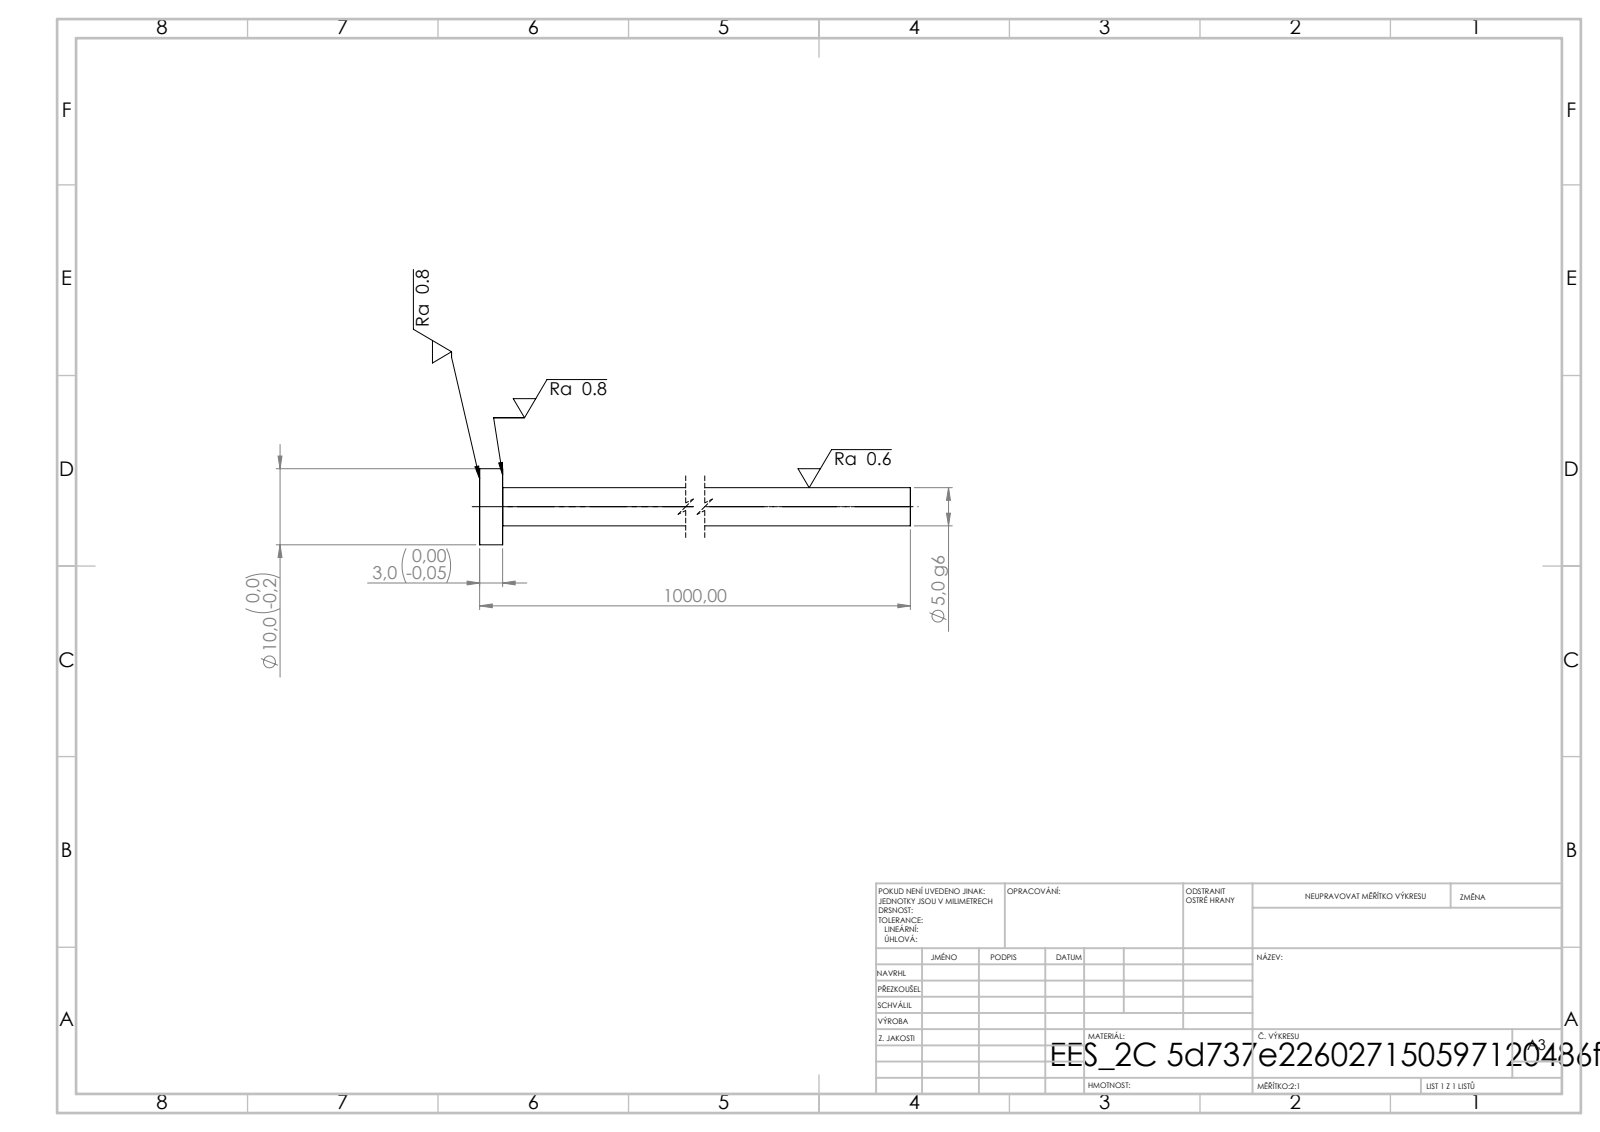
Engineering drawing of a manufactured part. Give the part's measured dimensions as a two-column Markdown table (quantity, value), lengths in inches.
| quantity | value |
| --- | --- |
| STEP written by | SolidWorks 2019 (CONFIG_CONTROL_DESIGN) |
| units | inches |
| bodies | 1 solid, 7 faces (3 planar, 4 cylindrical, 0 other) |
| overall size | 39.37 × 0.394 × 0.394 |
| volume | 1.209 in³ |
| surface area | 24.66 in² |
| round bosses / shafts (diameter × count) | 0.394 × 1, 0.197 × 1 |
| main face-to-face distances | 0.118, 39.37, 39.252 |
